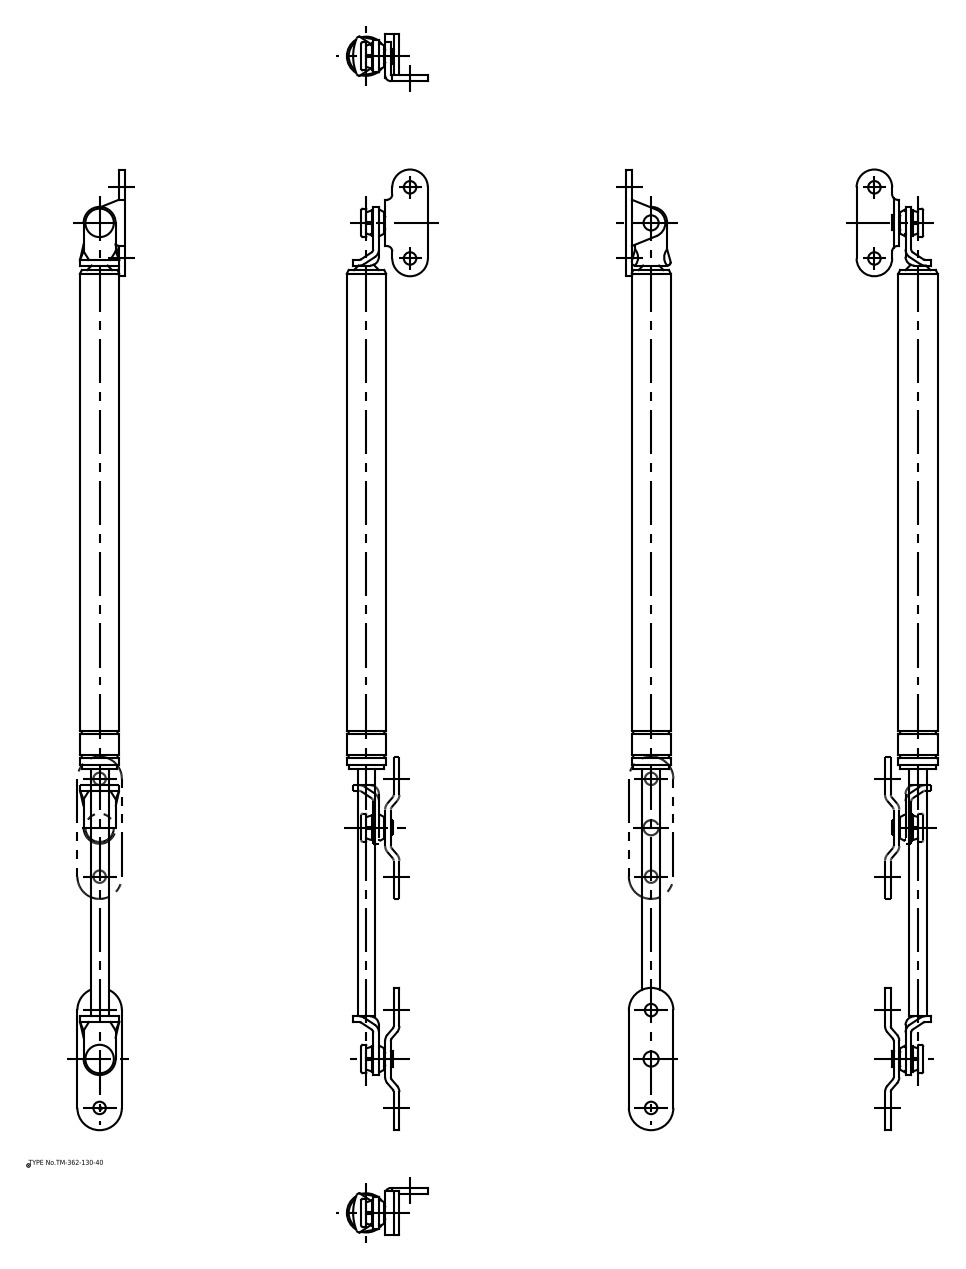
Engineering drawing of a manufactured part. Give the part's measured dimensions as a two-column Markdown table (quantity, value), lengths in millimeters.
| quantity | value |
| --- | --- |
| part name | ブッシュ; ブラケット(A); ブラケット(B); ボルト (+2 more) |
| STEP written by | spGate 16.7.1 (AUTOMOTIVE_DESIGN) |
| units | millimeters |
| bodies | 8 solids, 225 faces (113 planar, 84 cylindrical, 28 other) |
| overall size | 540 × 45.75 × 26.5 |
| volume | 136 350 mm³ |
| surface area | 40 348 mm² |
| round holes (diameter × count) | 7 × 4, 8.5 × 2 |
| round bosses / shafts (diameter × count) | 10 × 3, 16 × 2, 15 × 2, 13 × 2, 22.5 × 1, 22 × 1, 20 × 1 |
| partial cylindrical surfaces (radius × count) | 2 × 4, 5.2 × 4, 0.5 × 2, 4.4 × 2, 5 × 2, 9 × 2, 10 × 2, 12.5 × 2 |
| main face-to-face distances | 3.2, 11.5, 6.7, 4.8, 14.7, 3.5, 8.3, 8, 9.9, 1.6 |
| hole center spacings | 27.5, 40, 55, 442.5, 470, 497.5 |
